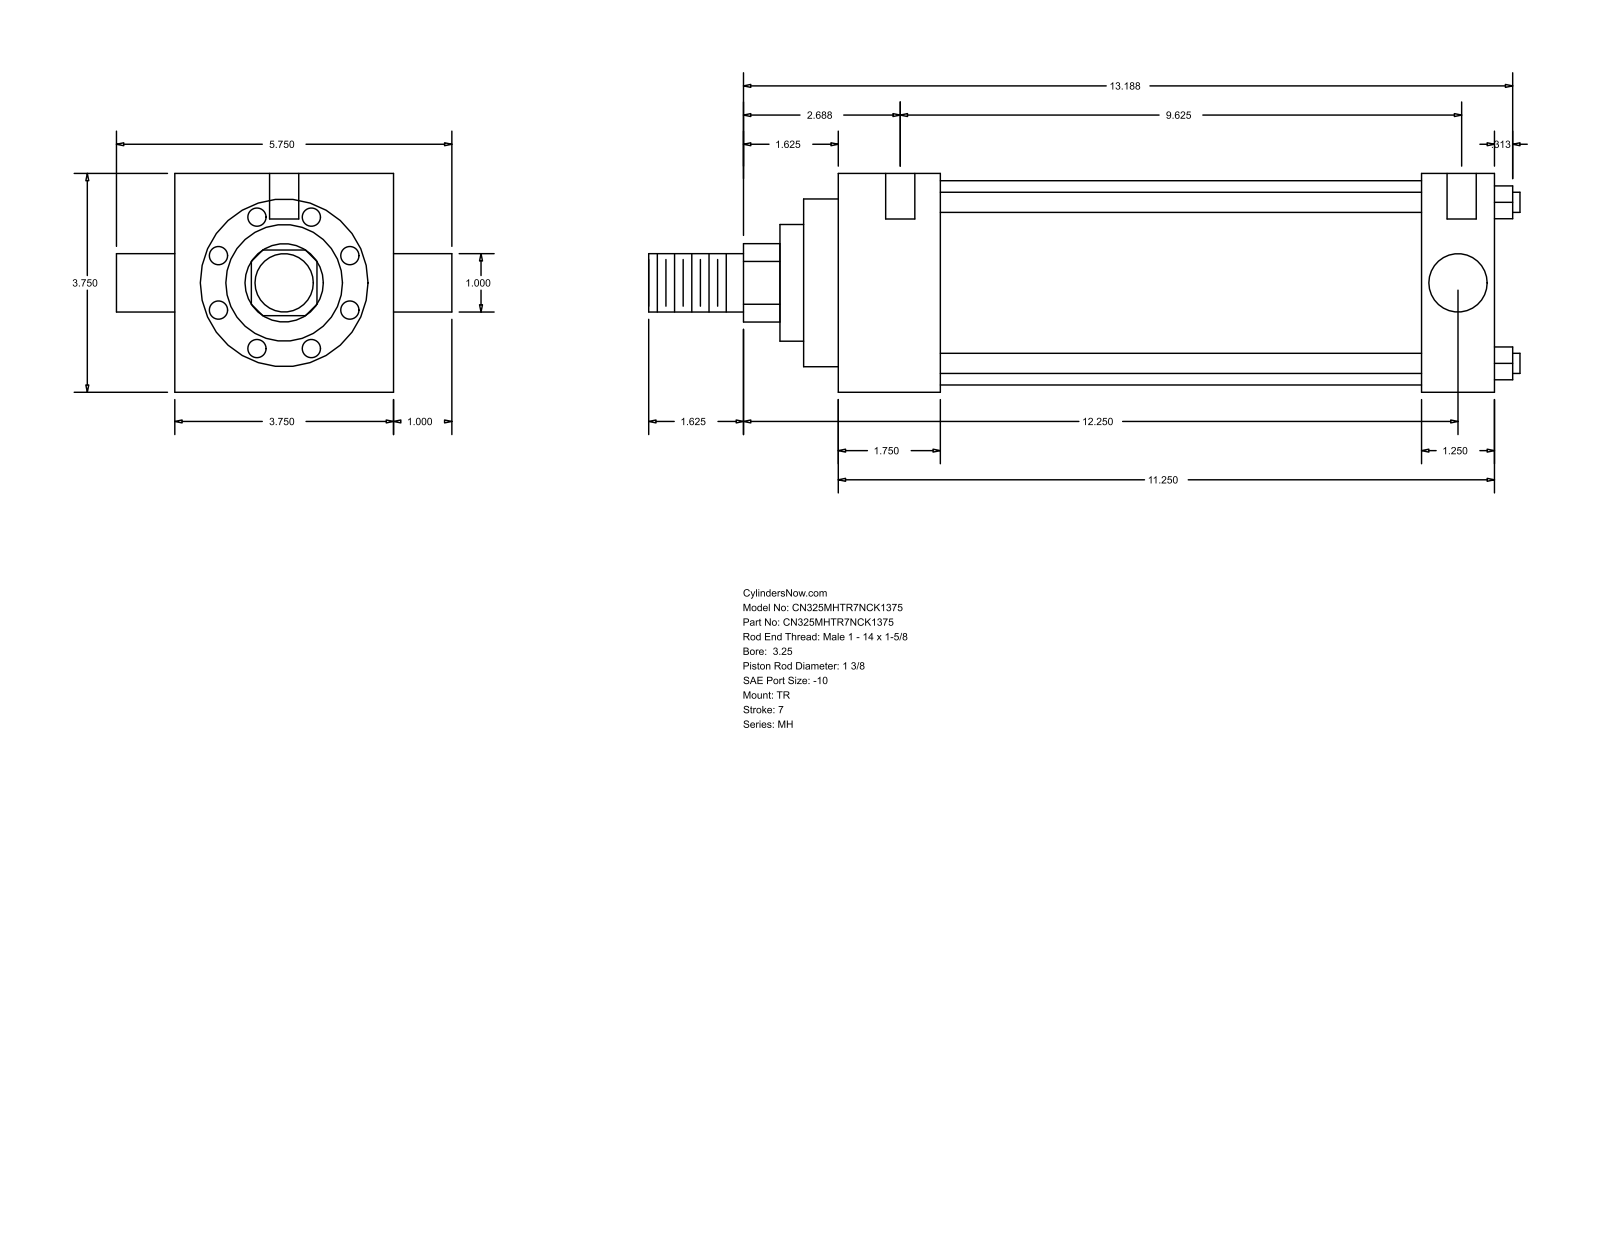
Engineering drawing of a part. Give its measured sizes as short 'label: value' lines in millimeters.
name: MH_TR__0325_1.375
written by: GSSL Pune (CONFIG_CONTROL_DESIGN)
unit: mm
bodies: 0 solids, 86 faces (61 planar, 25 cylindrical, 0 other)
size: 379.41 × 146.05 × 95.25
holes: 3× ⌀5.56, 2× ⌀12.7
bosses: 4× ⌀8.76, 2× ⌀25.4, 1× ⌀88.9, 1× ⌀73.03, 1× ⌀50.8, 1× ⌀34.92
rounds: 1× R17.06
face distances: 95.24, 285.75, 44.45, 254, 209.55, 241.3, 31.75, 15.08, 59.53, 269.08
hole spacings: 1.59, 4.76, 244.48, 246.07, 249.24, 250.83
